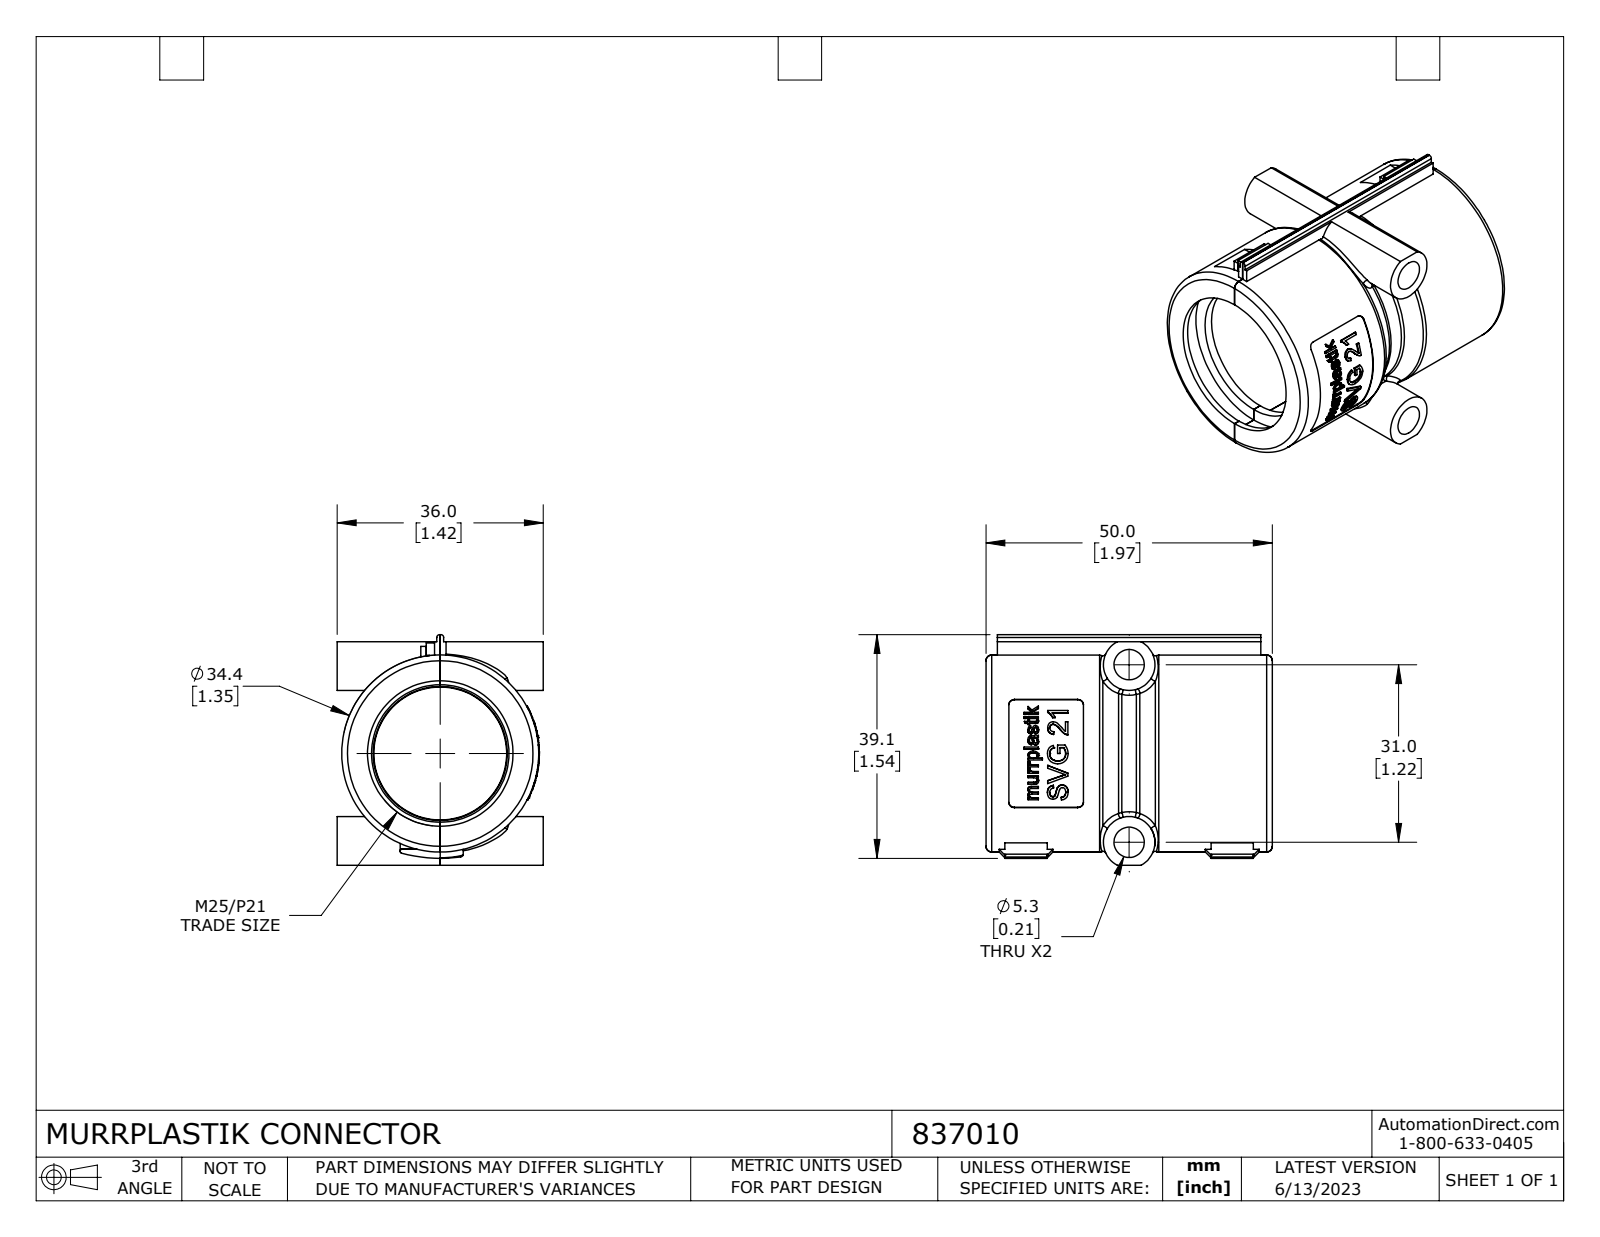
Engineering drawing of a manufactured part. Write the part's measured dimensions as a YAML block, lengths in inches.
part_name: "837010"
step_written_by: "SolidWorks 2021 (CONFIG_CONTROL_DESIGN)"
units: inches
bodies: {solids: 2, faces: 479, planar: 217, cylindrical: 80, other: 182}
overall_size: [1.969, 1.585, 1.417]
volume: 1.08
surface_area: 24.64
round_holes:
  - {diameter: 0.209, count: 2}
  - {diameter: 0.913, count: 1}
  - {diameter: 0.945, count: 1}
  - {diameter: 1, count: 1}
  - {diameter: 1.122, count: 1}
round_bosses_or_shafts:
  - {diameter: 0.354, count: 2}
  - {diameter: 1.354, count: 1}
partial_cylinders:
  - {radius: 0.02, count: 3}
  - {radius: 0.012, count: 2}
  - {radius: 0.039, count: 1}
  - {radius: 0.587, count: 1}
  - {radius: 0.673, count: 1}
  - {radius: 0.681, count: 1}
  - {radius: 1.024, count: 1}
face_to_face_distances: [1.535, 0.063, 0.043, 0.248, 0.185, 1.72, 1.783, 1.969, 0.142, 1.925]
hole_center_spacings: [1.22]
